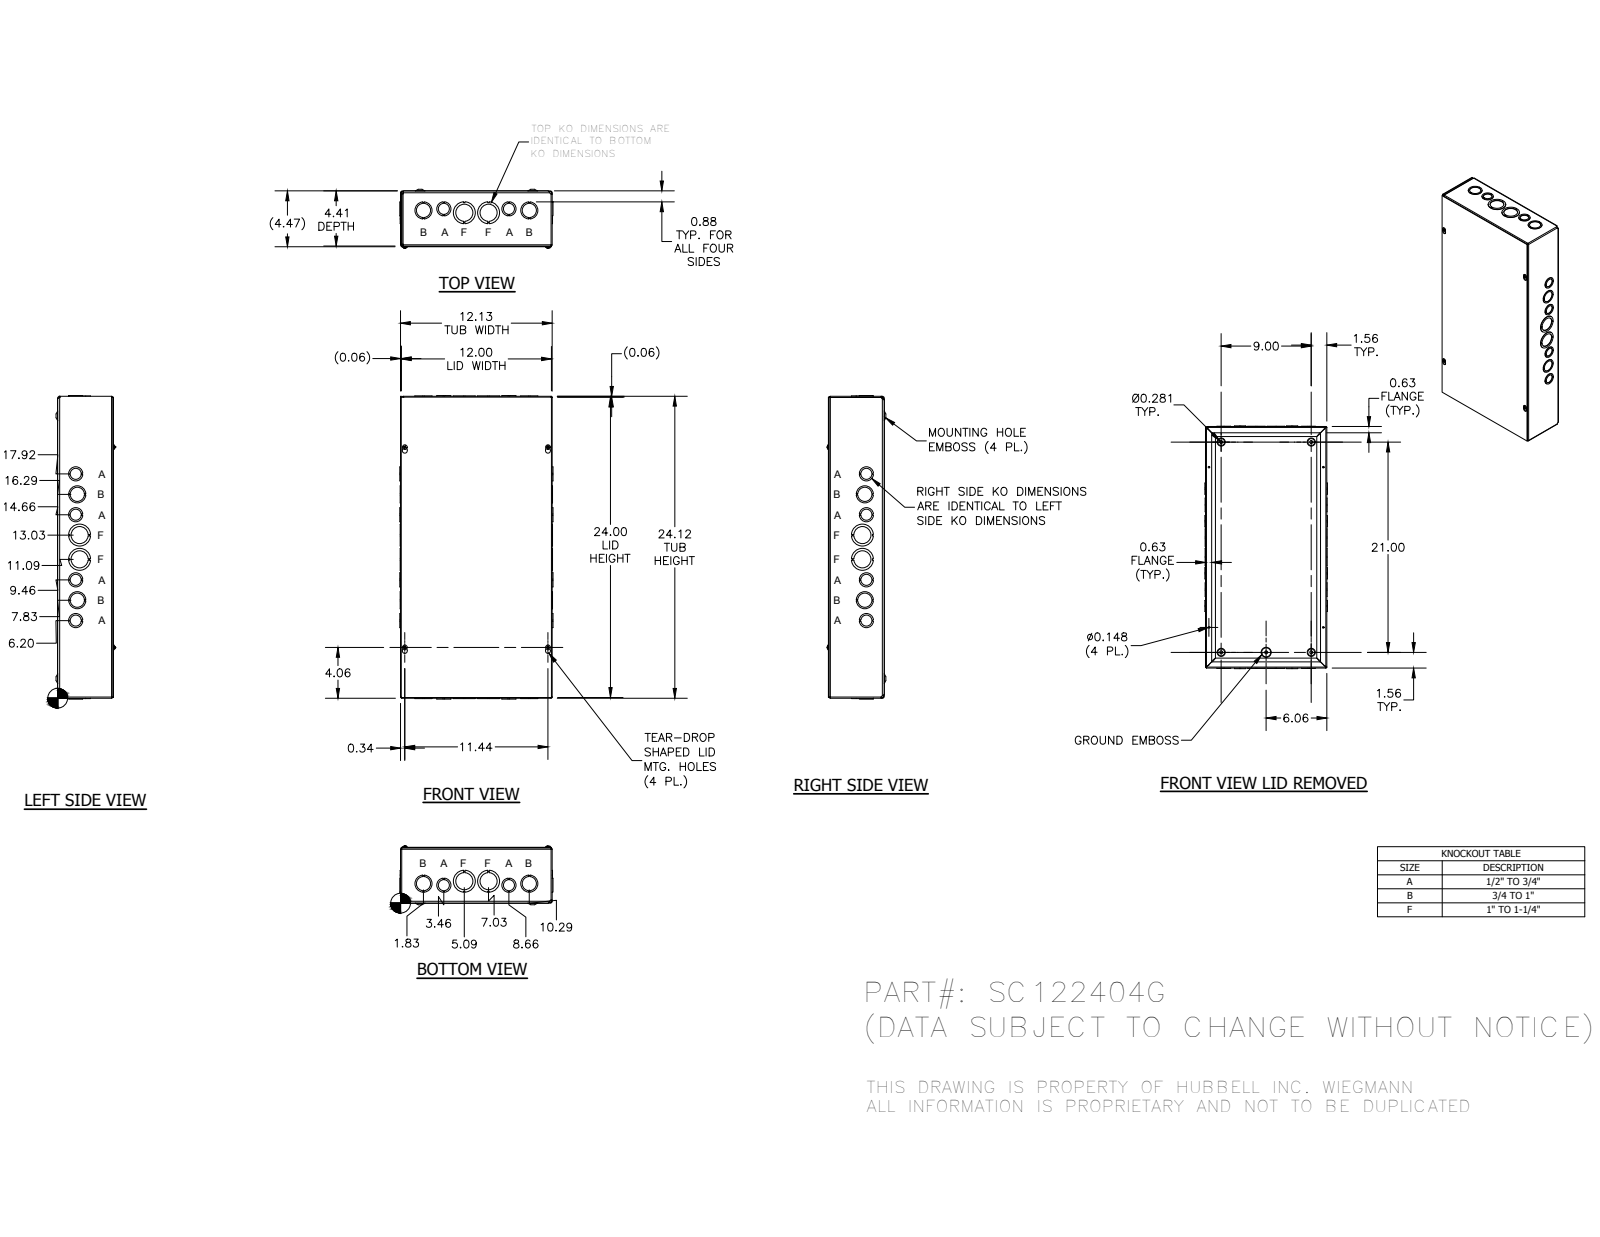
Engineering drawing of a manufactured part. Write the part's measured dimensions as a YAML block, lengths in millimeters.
part_name: "SC1224GBKP; SC122404GWRA; SC1224GLID; 34056 (+1 more)"
step_written_by: "Autodesk Inventor 2014 (AUTOMOTIVE_DESIGN)"
units: millimeters
bodies: {solids: 30, faces: 1142, planar: 750, cylindrical: 241, other: 151}
overall_size: [615.92, 311.12, 119.2]
round_holes:
  - {diameter: 28.57, count: 10}
  - {diameter: 34.92, count: 8}
  - {diameter: 22.22, count: 6}
  - {diameter: 3.76, count: 4}
  - {diameter: 7.62, count: 4}
  - {diameter: 44.45, count: 4}
  - {diameter: 4.19, count: 1}
round_bosses_or_shafts:
  - {diameter: 9.75, count: 4}
  - {diameter: 4.17, count: 4}
  - {diameter: 5.8, count: 1}
partial_cylinders:
  - {radius: 0.79, count: 8}
  - {radius: 2.37, count: 8}
  - {radius: 1.4, count: 4}
  - {radius: 1.57, count: 4}
  - {radius: 2.38, count: 4}
  - {radius: 2.79, count: 4}
  - {radius: 2.97, count: 4}
  - {radius: 3.15, count: 4}
face_to_face_distances: [1.57, 110.32, 111.89, 1.59, 111.91, 113.48, 1.58, 307.98, 306.4, 306.41]
hole_center_spacings: [41.52, 42.15, 82.94, 91.03, 132.17, 173.51, 470.92, 536.82]
